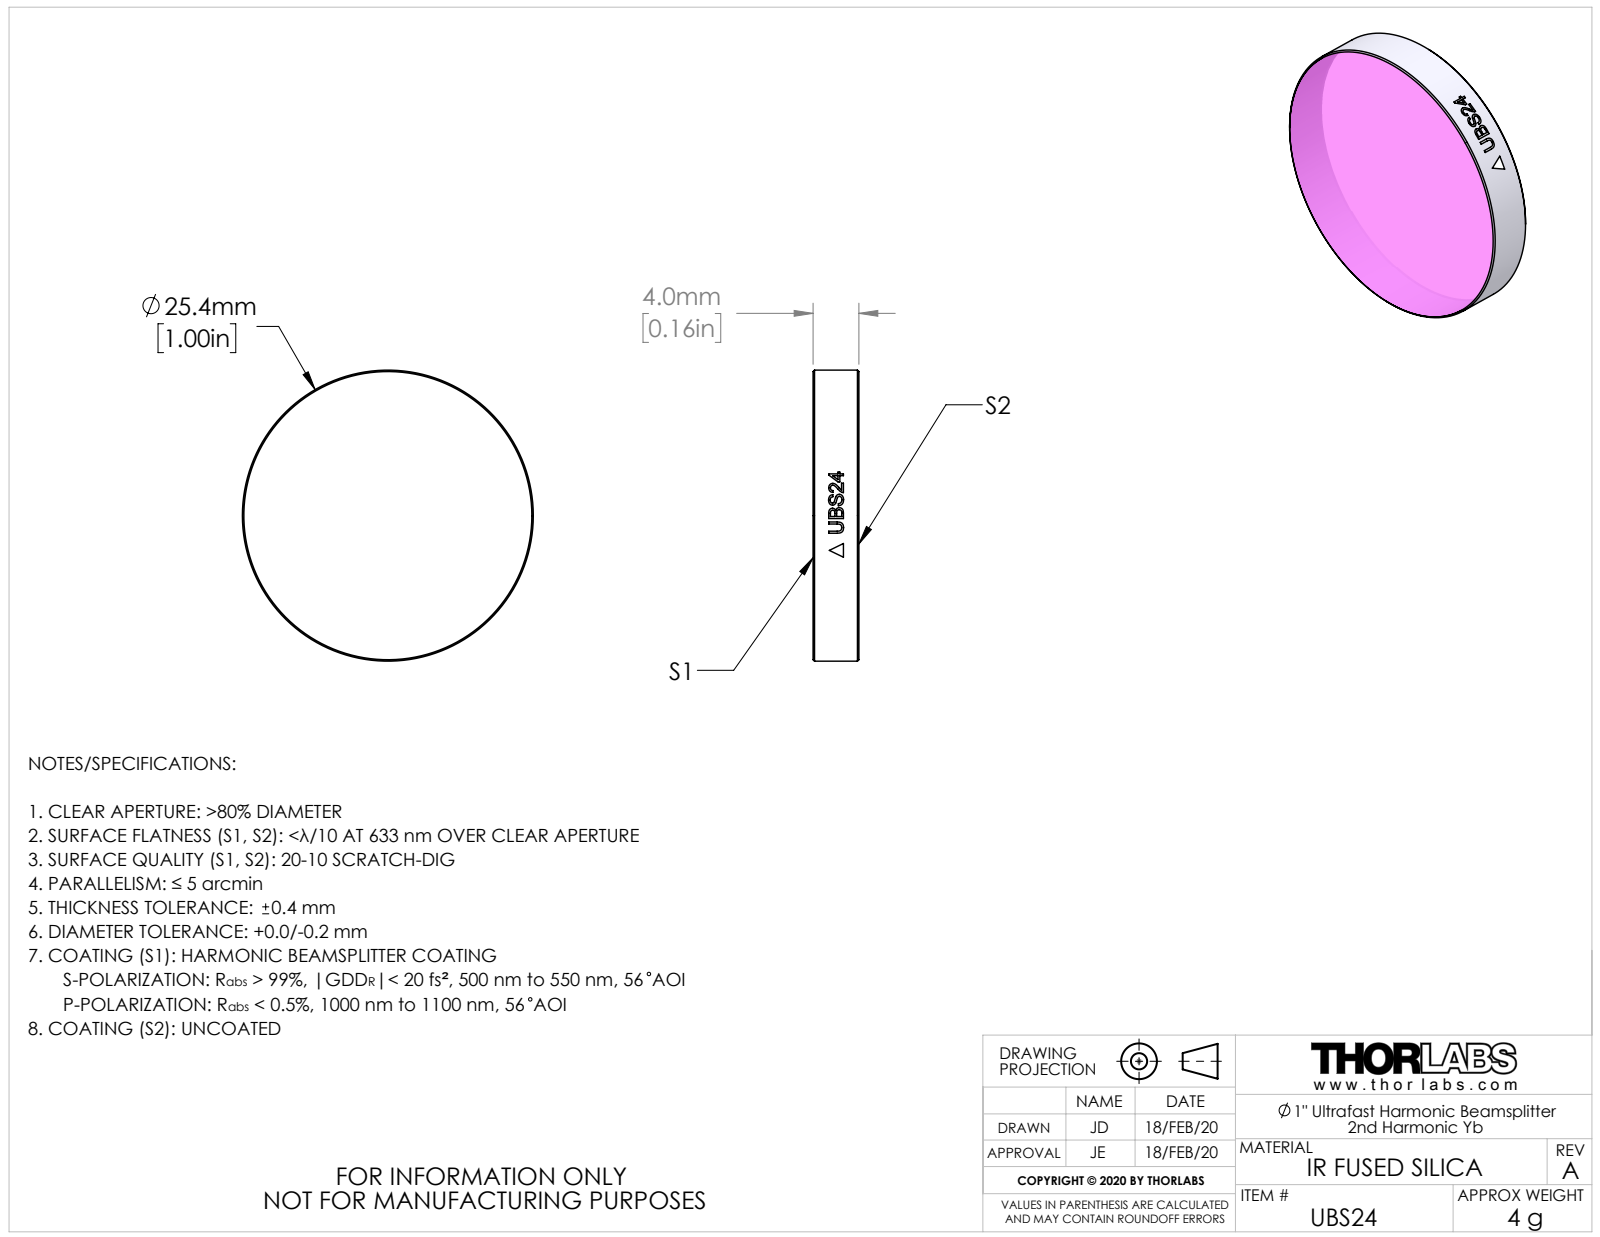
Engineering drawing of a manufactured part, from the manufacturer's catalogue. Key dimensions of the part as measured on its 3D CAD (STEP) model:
Part name (STEP PRODUCT): TTN208338-E0W
STEP written by: SolidWorks 2018 (AUTOMOTIVE_DESIGN)
Units: inches
Bodies: 1 solid, 24 faces (2 planar, 18 cylindrical, 4 other)
Overall size (bounding box): 1 × 1 × 0.157
Volume: 0.124 in³ · Surface area: 2.047 in²
Round holes (diameter × count): ⌀0.99 ×1
Round bosses / shafts (diameter × count): ⌀1 ×1
Main face-to-face distances: 0.157
